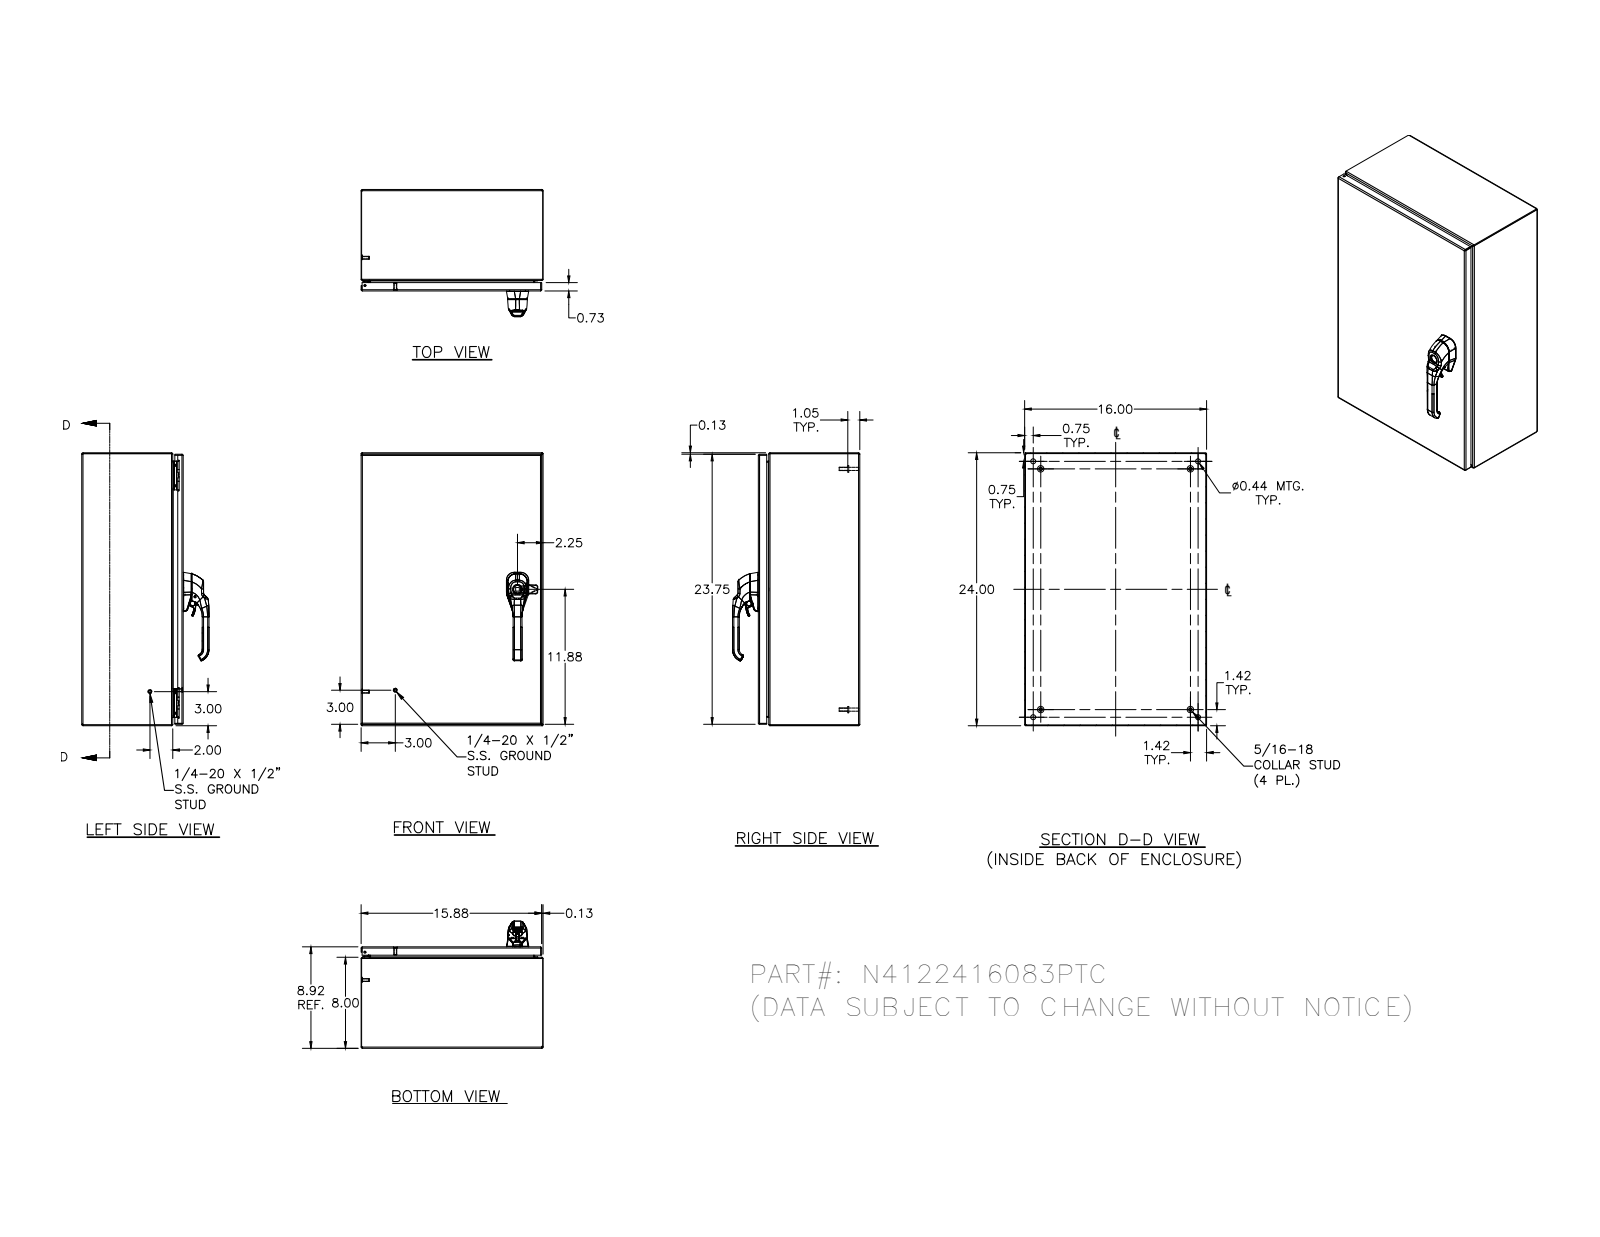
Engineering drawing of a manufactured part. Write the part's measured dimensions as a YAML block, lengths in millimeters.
part_name: "N4122416083PTC"
step_written_by: "SolidWorks 2018 (AUTOMOTIVE_DESIGN)"
units: millimeters
bodies: {solids: 29, faces: 1333, planar: 433, cylindrical: 495, other: 405}
overall_size: [609.6, 406.4, 281.8]
volume: 2061000
surface_area: 2061000
round_holes:
  - {diameter: 4.8, count: 5}
  - {diameter: 2.4, count: 4}
  - {diameter: 3.9, count: 4}
  - {diameter: 4.2, count: 4}
  - {diameter: 4.4, count: 4}
  - {diameter: 11.1, count: 4}
  - {diameter: 4, count: 2}
  - {diameter: 4.7, count: 1}
  - {diameter: 10.5, count: 1}
round_bosses_or_shafts:
  - {diameter: 6.4, count: 10}
  - {diameter: 14.3, count: 4}
  - {diameter: 9.1, count: 4}
  - {diameter: 8.1, count: 4}
  - {diameter: 7.6, count: 4}
  - {diameter: 7, count: 4}
  - {diameter: 6.5, count: 4}
  - {diameter: 4.2, count: 4}
partial_cylinders:
  - {radius: 0.8, count: 30}
  - {radius: 1.3, count: 26}
  - {radius: 2.7, count: 20}
  - {radius: 0.4, count: 18}
  - {radius: 3.2, count: 14}
  - {radius: 0.5, count: 11}
  - {radius: 0.8, count: 8}
  - {radius: 1.7, count: 8}
face_to_face_distances: [1.9, 224.6, 226.5, 404.5, 222.7, 607.7, 402.6, 406.4, 609.6, 605.8]
hole_center_spacings: [507.9, 0.4, 16.8, 524.7, 0.5, 12.7, 16.5, 16.7]
